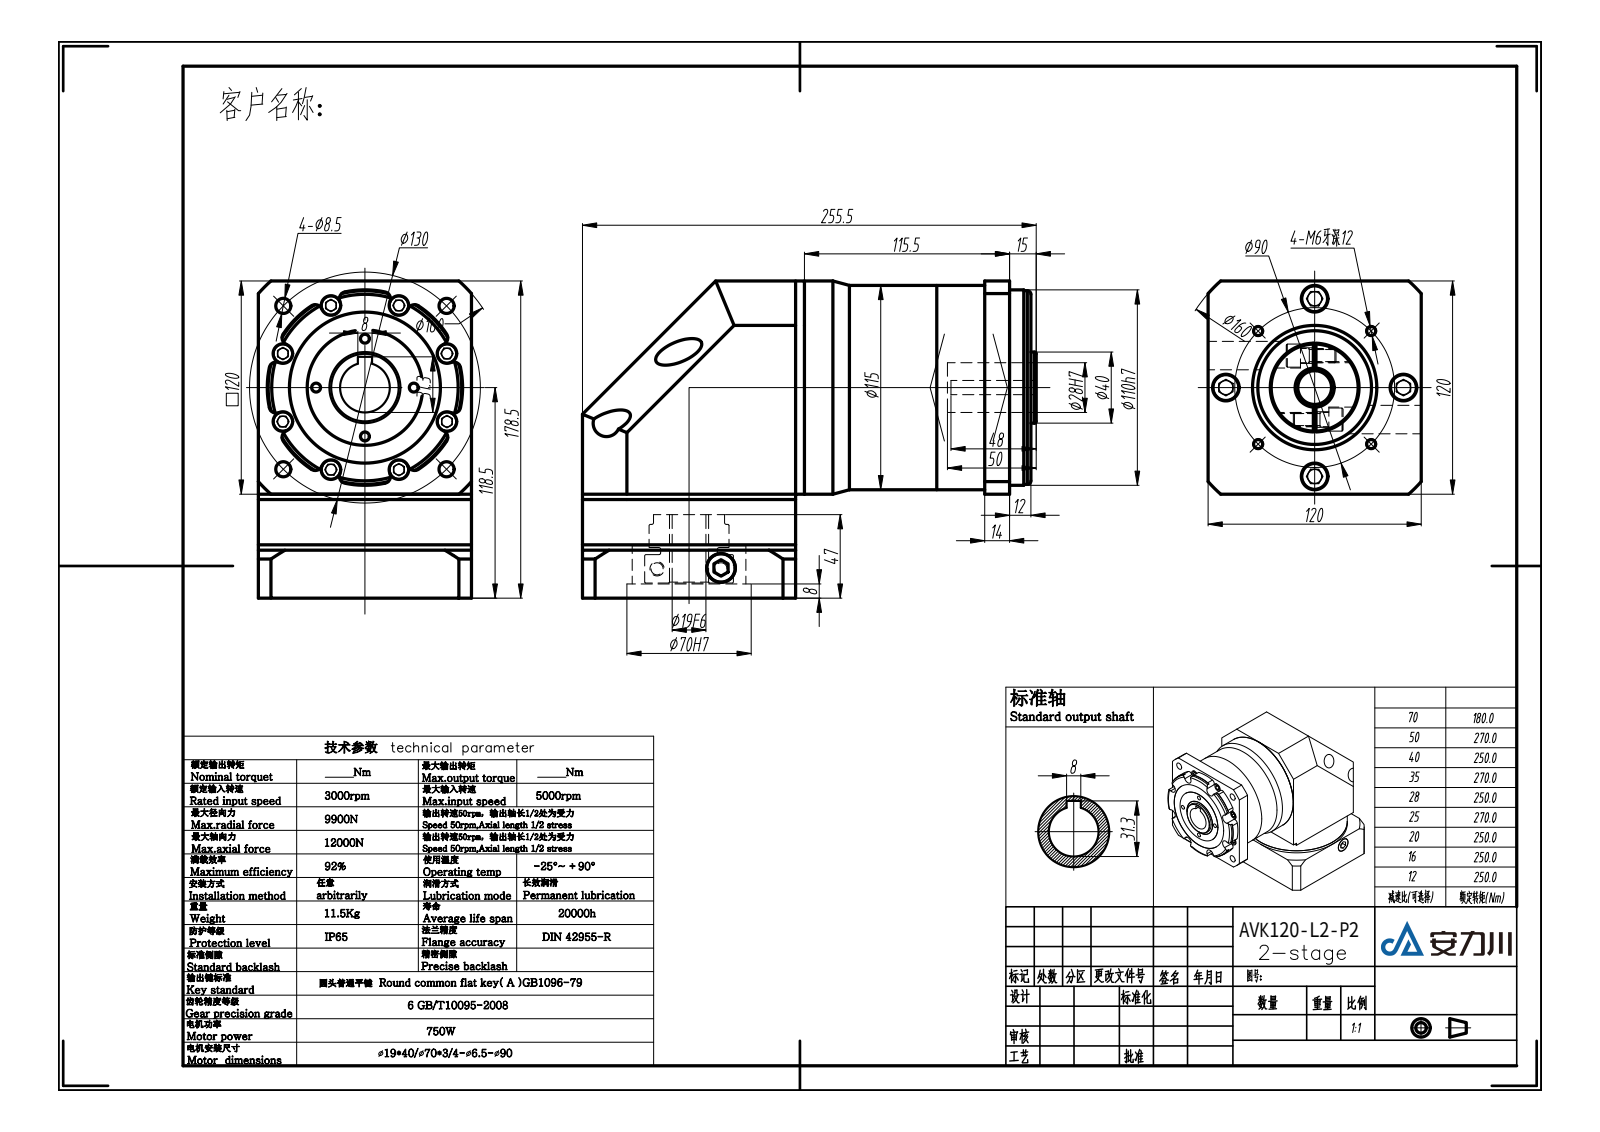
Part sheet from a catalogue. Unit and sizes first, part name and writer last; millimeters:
Units: millimetres
Overall size (bounding box): 255.5 × 178.5 × 120
Round holes (diameter × count): ⌀15 ×10, ⌀5 ×8, ⌀11 ×8, ⌀8.5 ×4, ⌀16 ×2, ⌀19 ×1, ⌀20 ×1, ⌀22 ×1, ⌀28 ×1, ⌀45.2 ×1, ⌀70 ×1, ⌀85 ×1
Round bosses / shafts (diameter × count): ⌀13 ×10, ⌀9.5 ×8, ⌀120 ×2, ⌀15.6 ×2, ⌀115 ×1, ⌀65 ×1, ⌀50 ×1, ⌀45 ×1
Partial cylindrical surfaces — rounded edges, fillets, slot ends (radius × count): R4 ×16, R80 ×2, R54.5 ×1, R55 ×1
Main face-to-face distances: 5, 25.5, 120, 49.17, 74.5, 79.5, 25.33, 30.33, 30, 55.5
Hole centre spacings: 39.29, 94.69, 26.74, 26.83, 36.65, 46.94, 49.53, 49.99
Volume: 3 271 000 mm³ · Surface area: 343 237 mm²
Bodies: 23 solids, 501 faces (278 planar, 198 cylindrical, 25 other)
Part name (STEP PRODUCT): VGZK115双级模型（19-40 70-3 4-6.5-90）
STEP written by: SolidWorks 2016 (AUTOMOTIVE_DESIGN)
